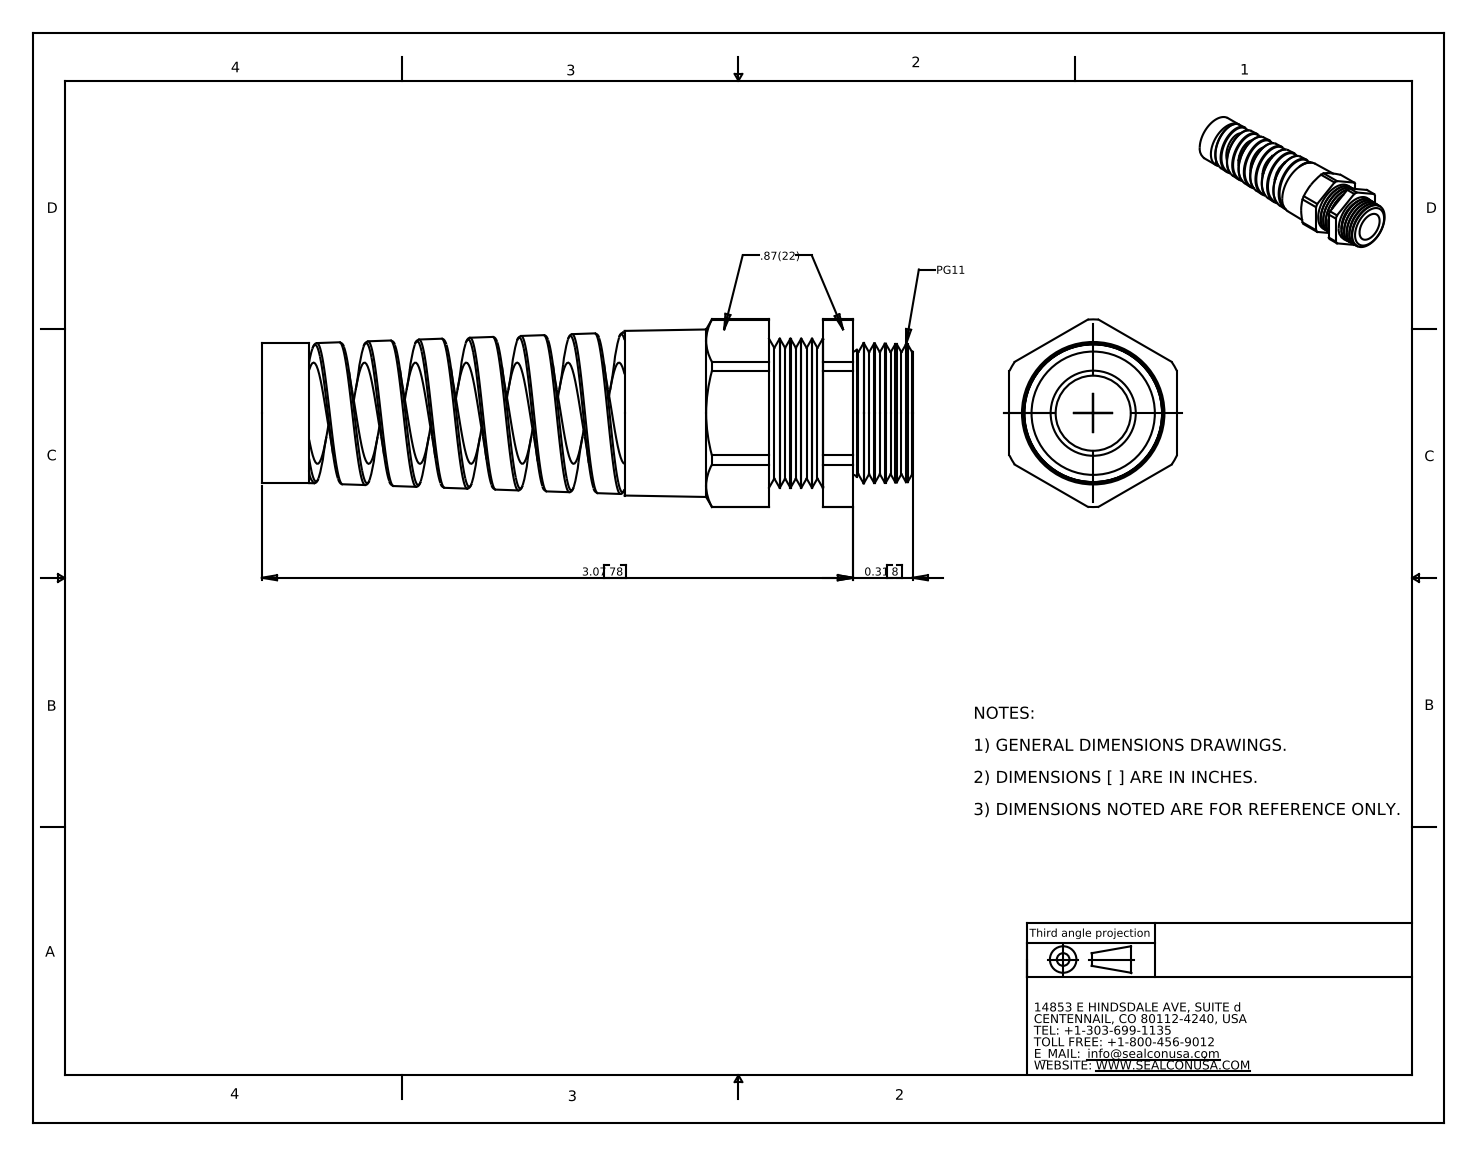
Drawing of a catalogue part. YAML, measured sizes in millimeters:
part_name: "CF11AA-GY"
step_written_by: "SolidWorks 2007 (CONFIG_CONTROL_DESIGN)"
units: millimeters
bodies: {solids: 1, faces: 153, planar: 19, cylindrical: 42, other: 92}
overall_size: [85.9, 24.7, 22.1]
volume: 14400
surface_area: 10780
round_holes:
  - {diameter: 9.9, count: 1}
  - {diameter: 13.4, count: 1}
round_bosses_or_shafts:
  - {diameter: 19.7, count: 1}
  - {diameter: 18.4, count: 1}
partial_cylinders:
  - {radius: 12.4, count: 1}
face_to_face_distances: [22.1, 30.1, 47.9, 78, 74.1, 26.2, 3.9, 66.9, 19.1, 7.1]
